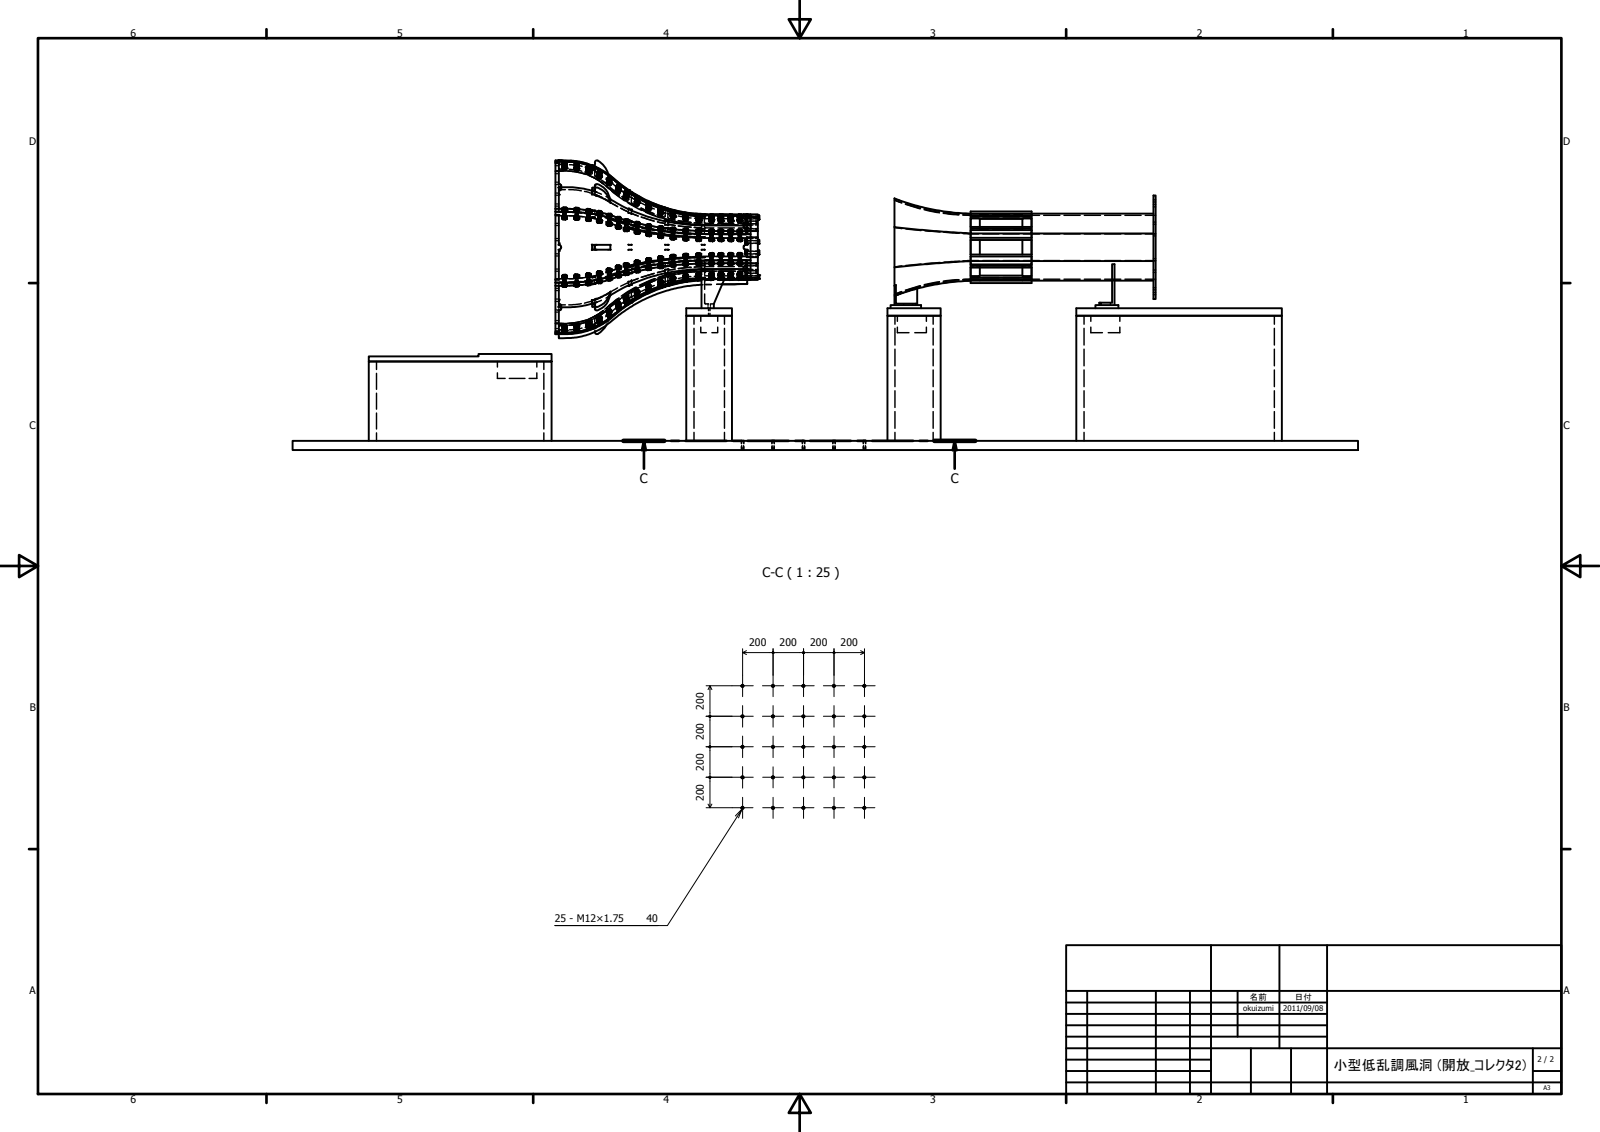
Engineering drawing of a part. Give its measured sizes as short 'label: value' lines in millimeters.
name: 小型低乱調風洞 (開放_コレクタ2)_rev3; 測定部台座; 測定部台座A; 測定部台座A_01 (+8 more)
written by: Autodesk Inventor 2013 (AUTOMOTIVE_DESIGN)
unit: mm
bodies: 366 solids, 9650 faces (4195 planar, 1200 cylindrical, 4255 other)
size: 6995 × 4490 × 1900
volume: 2 582 000 000 mm³; area: 109 700 000 mm²
holes: 150× ⌀19, 136× ⌀17.5, 136× ⌀20, 60× ⌀15, 32× ⌀16, 25× ⌀12, 16× ⌀18, 4× ⌀14, 4× ⌀14.5, 2× ⌀10.8
bosses: 136× ⌀30, 136× ⌀20, 25× ⌀15, 16× ⌀24, 8× ⌀16, 1× ⌀680
rounds: 153× R7, 16× R13, 12× R16, 8× R6, 8× R150
face distances: 60, 50, 300, 350, 112.5, 927.5, 815, 890, 880, 820
hole spacings: 200, 447.21, 85, 282.84, 632.46, 400, 80, 721.11
